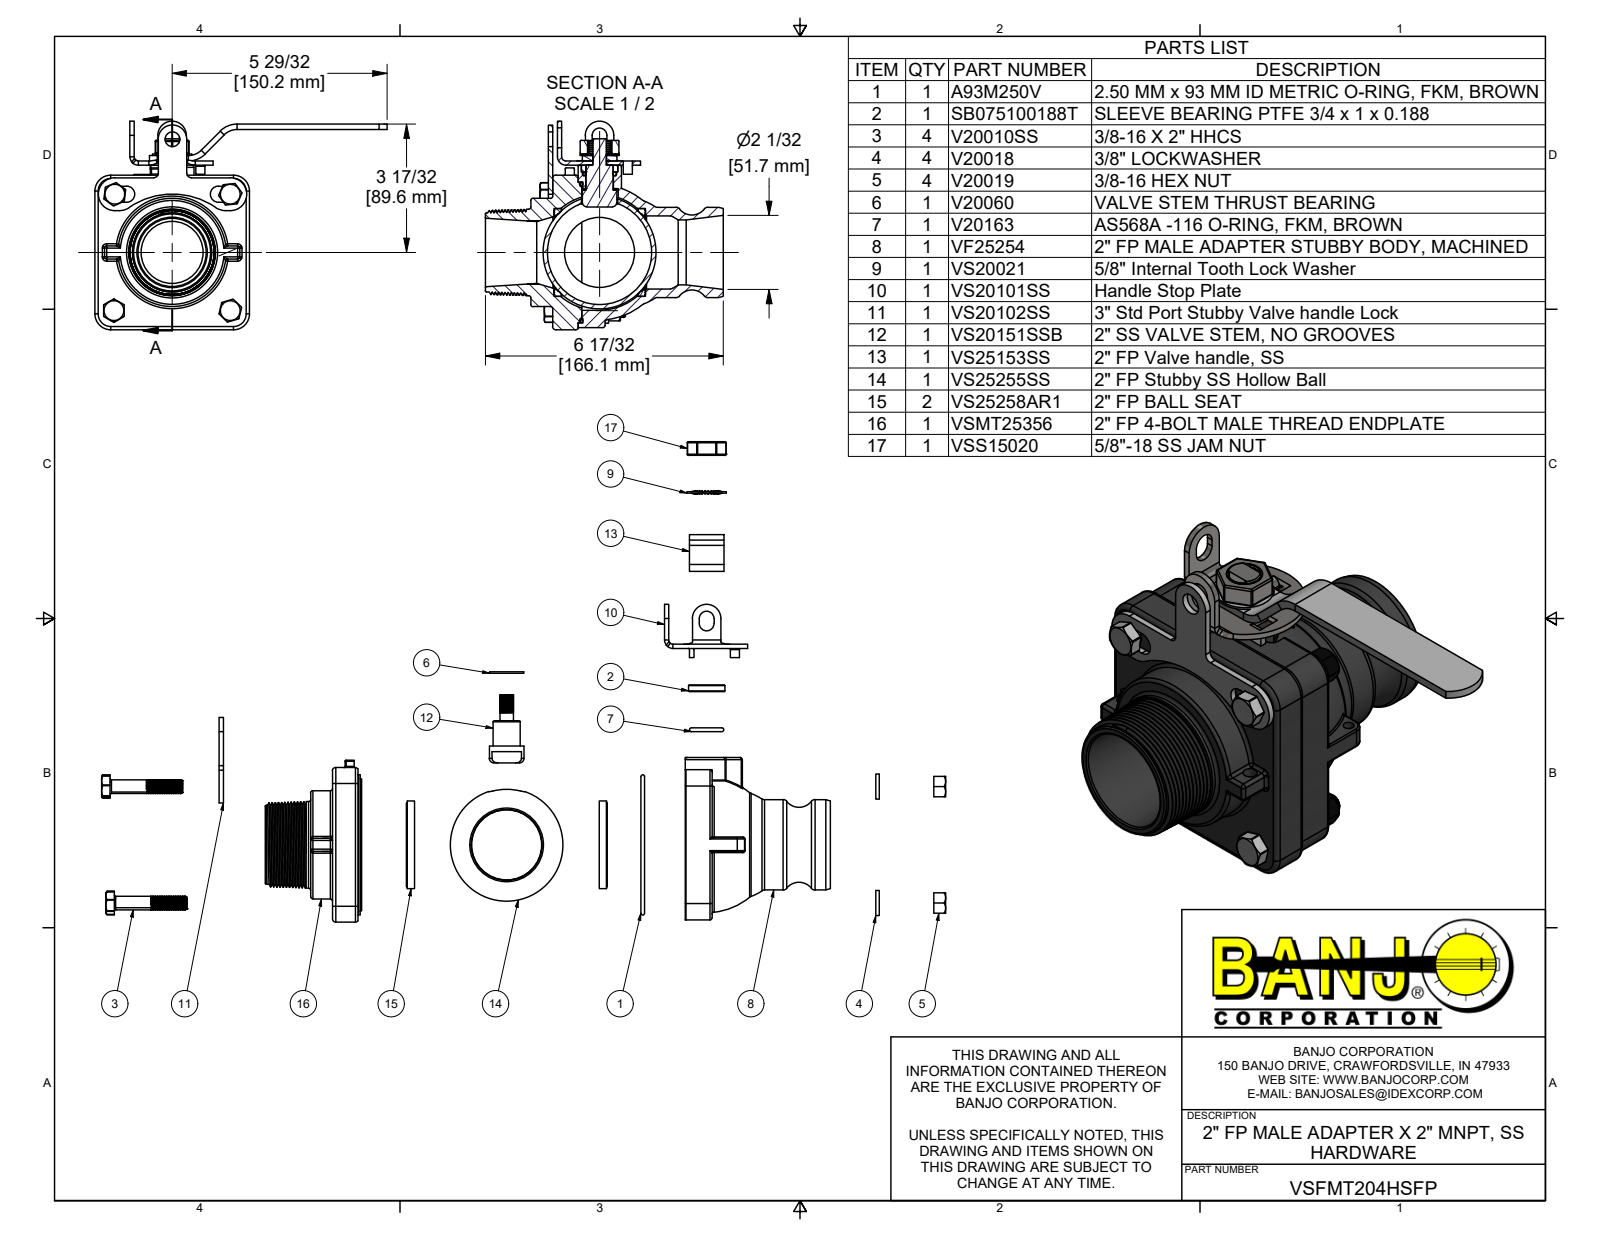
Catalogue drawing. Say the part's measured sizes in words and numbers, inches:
The part is named "VSFMT204HSFP; VF25254; VF25254X; VSMT25356 (+8 more)". Its 3-D file was written by "Autodesk Inventor 2022 (AUTOMOTIVE_DESIGN)". It is 28 solids with 1606 faces: 277 planar, 631 cylindrical and 698 other. Overall it measures 8.036 by 6.54 by 5.735 inches. Its volume is 32.95 cubic inches and its surface area 315.1 square inches. Round holes: 4 of diameter 0.307, 4 of diameter 0.385, 4 of diameter 0.44, 4 of diameter 0.455, 2 of diameter 0.2, 2 of diameter 0.26, 1 of diameter 0.375, 1 of diameter 0.406, 1 of diameter 0.662, 1 of diameter 0.75, 1 of diameter 0.76, 1 of diameter 0.86. Round bosses or shafts: 60 of diameter 0.324, 4 of diameter 0.687, 4 of diameter 0.375, 1 of diameter 3.85, 1 of diameter 3.625, 1 of diameter 2.975, 1 of diameter 2.481, 1 of diameter 2.412. Partial cylindrical surfaces (rounded edges, fillets, slot ends): 40 of radius 0.03, 29 of radius 0.06, 8 of radius 0.09, 8 of radius 0.162, 6 of radius 0.45, 4 of radius 0.118, 4 of radius 0.203, 4 of radius 0.32. The main face-to-face distances are 0.7, 0.06, 4.19, 0.15, 0.8, 0.1, 0.862, 0.64, 1.44, 0.74. The hole center spacings are 2.263, 3.2, 2.041, 2.214, 2.341, 4.202, 4.526, 2.192.
